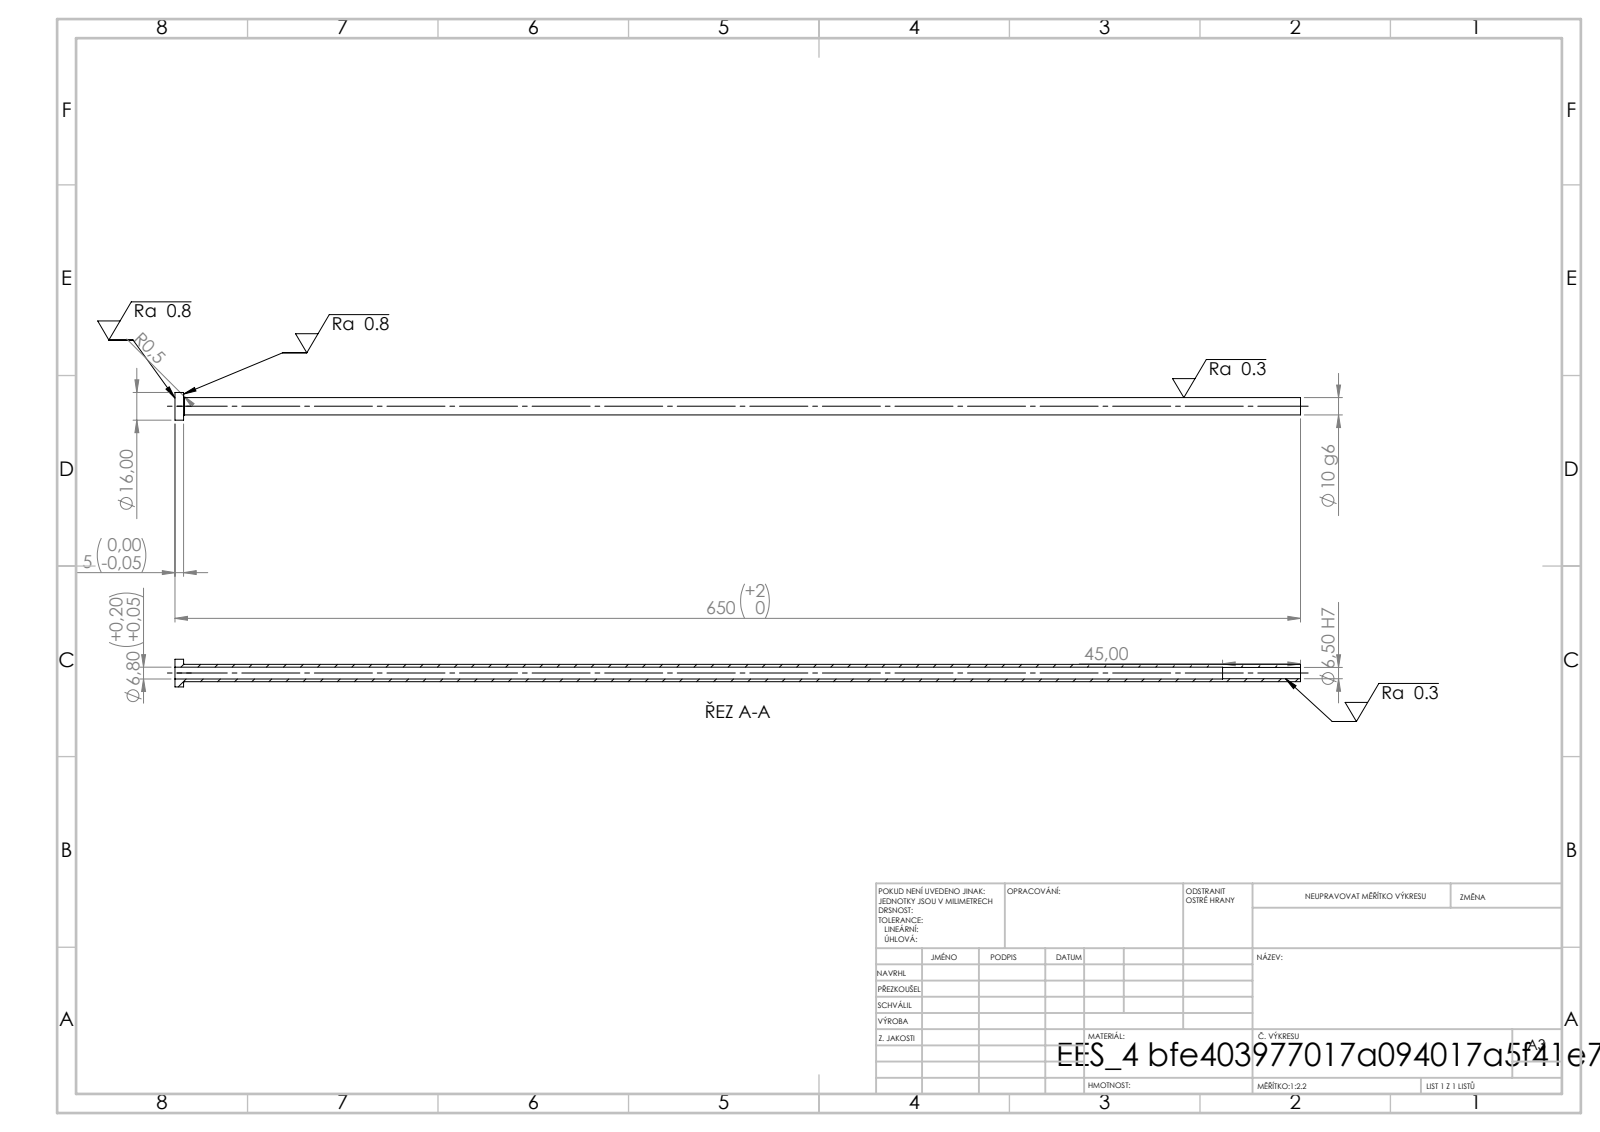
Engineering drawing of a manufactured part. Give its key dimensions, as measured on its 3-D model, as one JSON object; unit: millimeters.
{"step_written_by": "SolidWorks 2019 (CONFIG_CONTROL_DESIGN)", "units": "millimeters", "bodies": {"solids": 1, "faces": 14, "planar": 4, "cylindrical": 8, "other": 2}, "overall_size": [650, 16, 16], "volume_mm3": 28200, "surface_area_mm2": 34687, "round_holes": [[6.5, 1], [6.8, 1]], "round_bosses_or_shafts": [[16, 1], [10, 1]], "face_to_face_distances": [5, 650, 645, 605, 600, 45]}
